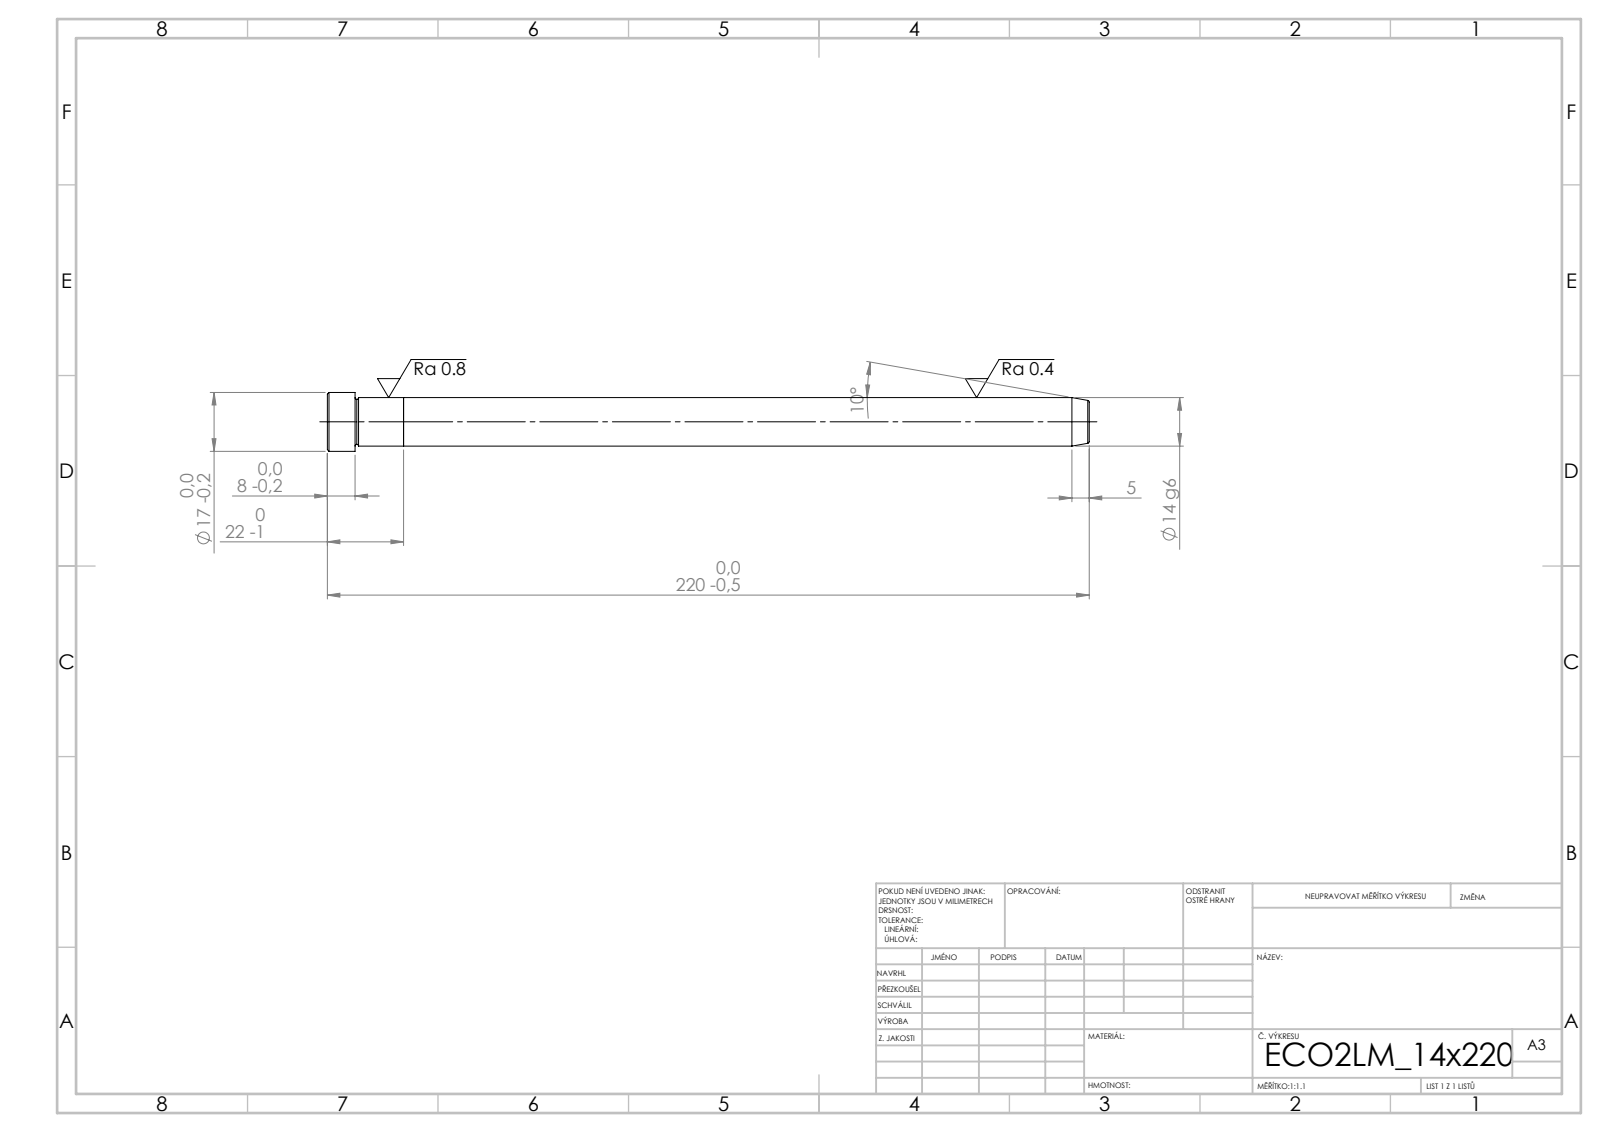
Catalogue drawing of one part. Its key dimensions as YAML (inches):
step_written_by: "SolidWorks 2019 (CONFIG_CONTROL_DESIGN)"
units: inches
bodies: {solids: 2, faces: 21, planar: 5, cylindrical: 6, other: 10}
overall_size: [8.661, 0.669, 0.669]
volume: 2.095
surface_area: 16.22
round_bosses_or_shafts:
  - {diameter: 0.669, count: 1}
  - {diameter: 0.551, count: 1}
face_to_face_distances: [0.866, 7.795, 8.661, 8.346, 0.551, 0.315]
